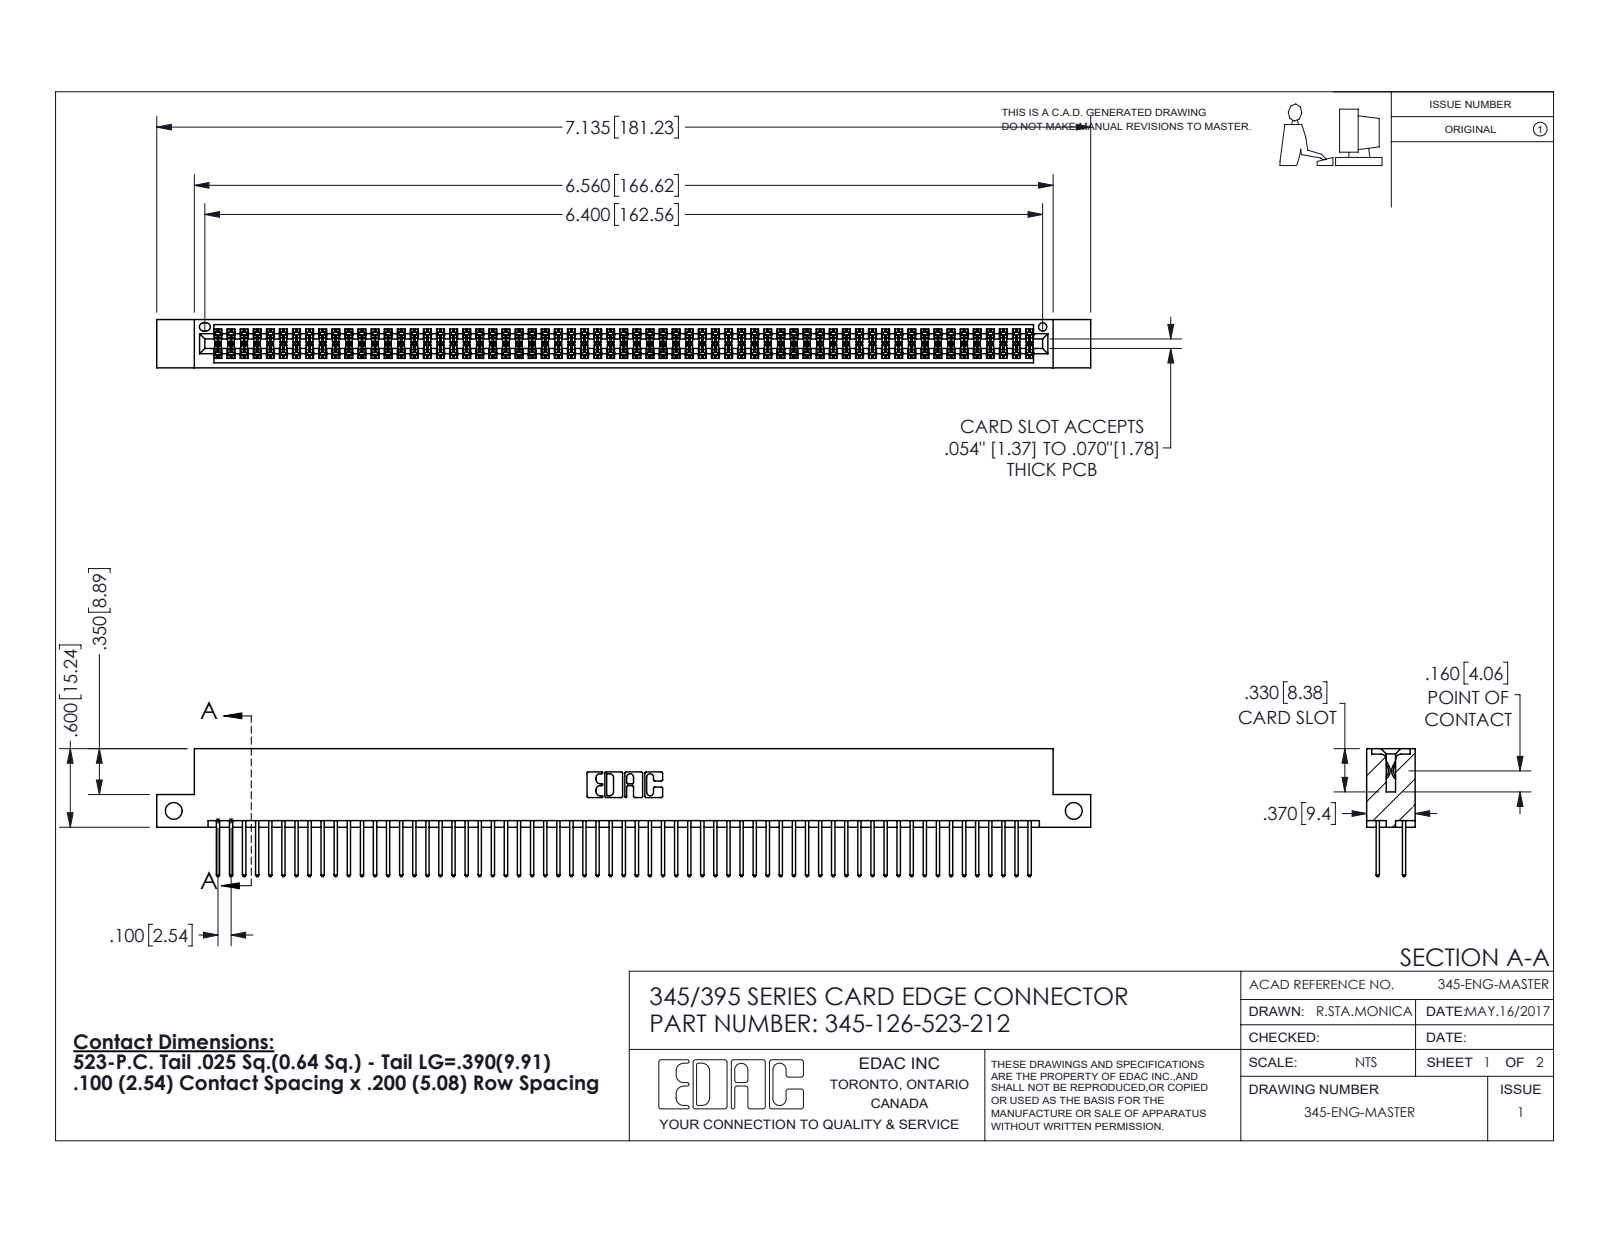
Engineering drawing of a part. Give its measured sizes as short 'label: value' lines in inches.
name: 345-292-001_345-293-123; 345 Part_Flush Mounting Lugs - Side Mount; 345-126-523-212
written by: SolidWorks 2016 (CONFIG_CONTROL_DESIGN)
unit: in
bodies: 127 solids, 6426 faces (4238 planar, 2188 cylindrical, 0 other)
size: 7.135 × 0.977 × 0.37
volume: 1.097 in³; area: 43.39 in²
holes: 2× ⌀0.128, 1× ⌀0.064
rounds: 189× R0.006, 126× R0.01, 22× R0.01, 6× R0.007, 6× R0.031, 3× R0.026, 2× R0.014, 2× R0.019
face distances: 0.298, 0.072, 0.2, 0.098, 0.272, 0.025, 0.37, 0.225, 0.175, 0.149
hole spacings: 6.875
